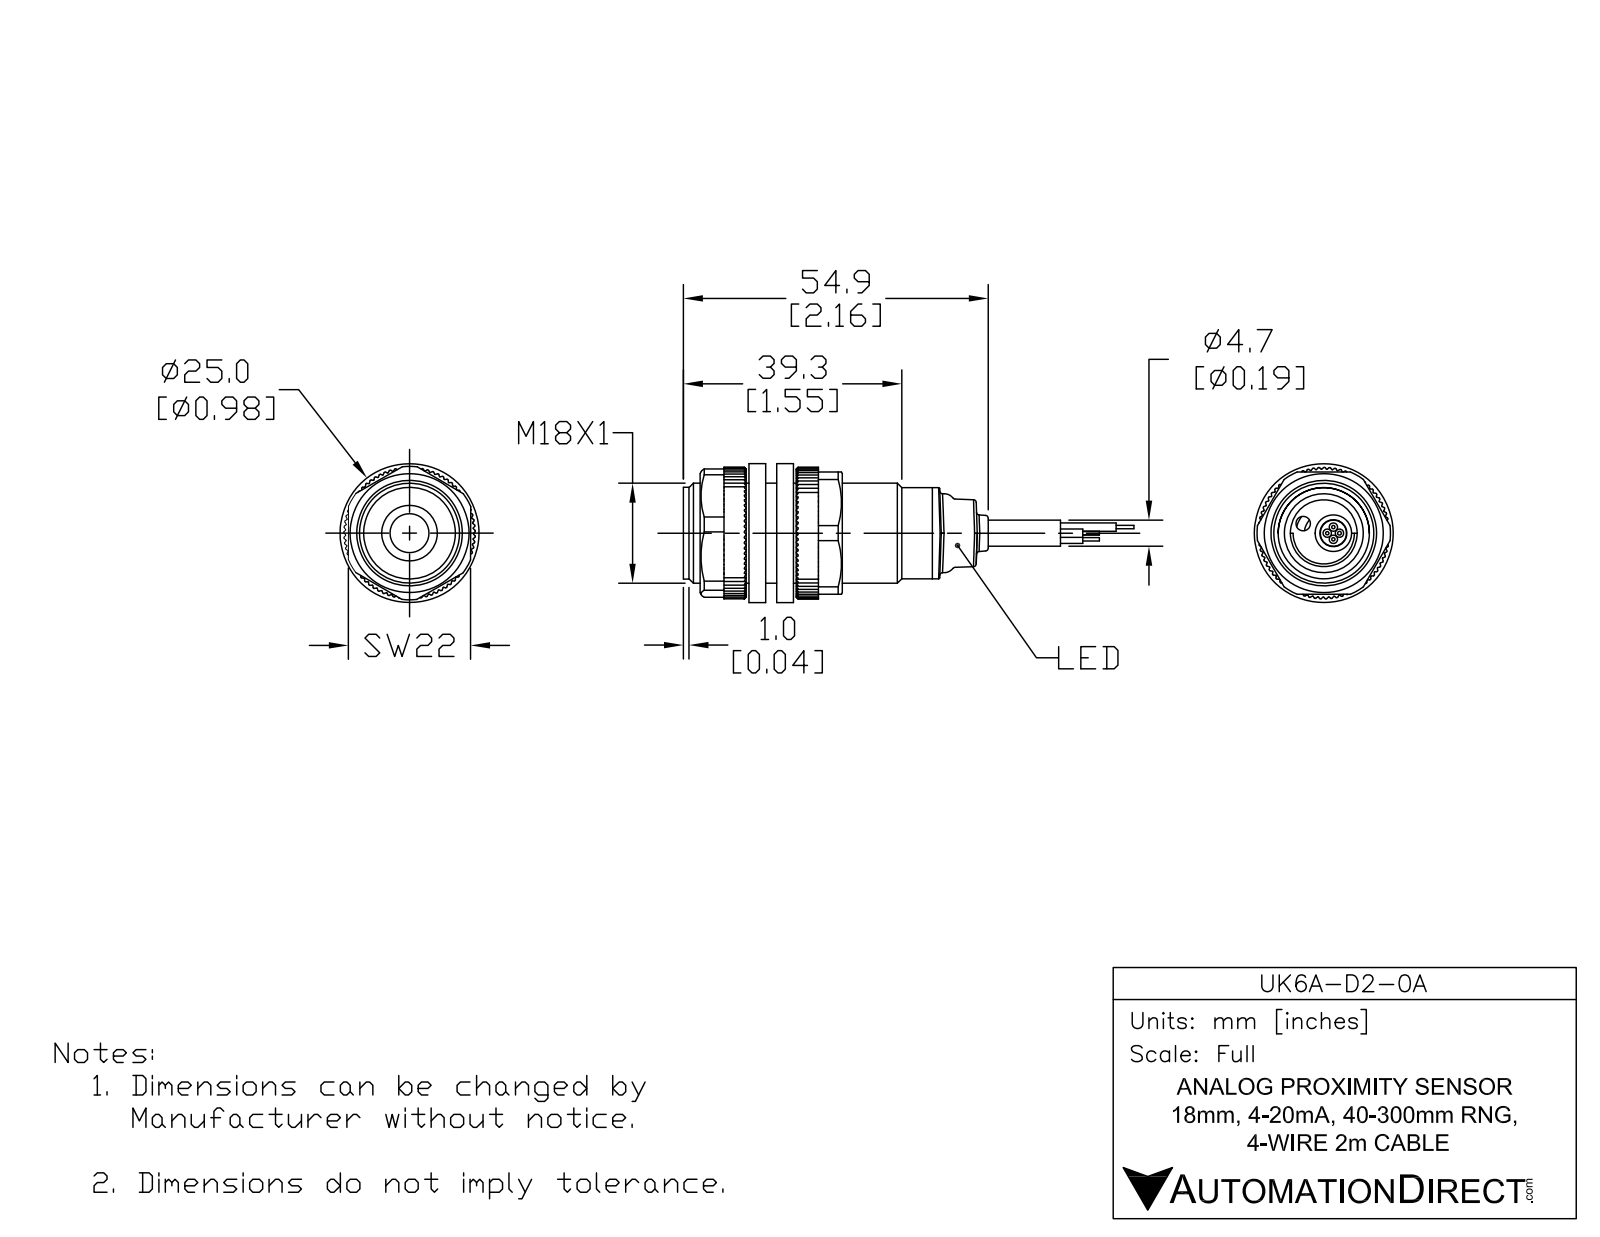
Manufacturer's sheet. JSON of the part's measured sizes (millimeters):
{"part_name": "UK6A-D2-0A", "step_written_by": "SolidWorks 2017 (AUTOMOTIVE_DESIGN)", "units": "millimeters", "bodies": {"solids": 4, "faces": 62, "planar": 14, "cylindrical": 19, "other": 29}, "overall_size": [89.8, 18, 18], "volume_mm3": 12900, "surface_area_mm2": 4795, "round_holes": [[4.7, 1], [9.5, 1]], "round_bosses_or_shafts": [[18, 1], [16.4, 1], [15.8, 1], [14.2, 1]], "partial_cylinders_radius": [[0.2, 1], [0.5, 1]], "face_to_face_distances": [43.8, 1, 44.8, 1, 44.8, 49.9, 49.8, 48.8, 5.1, 6.5], "hole_center_spacings": [1.7]}
